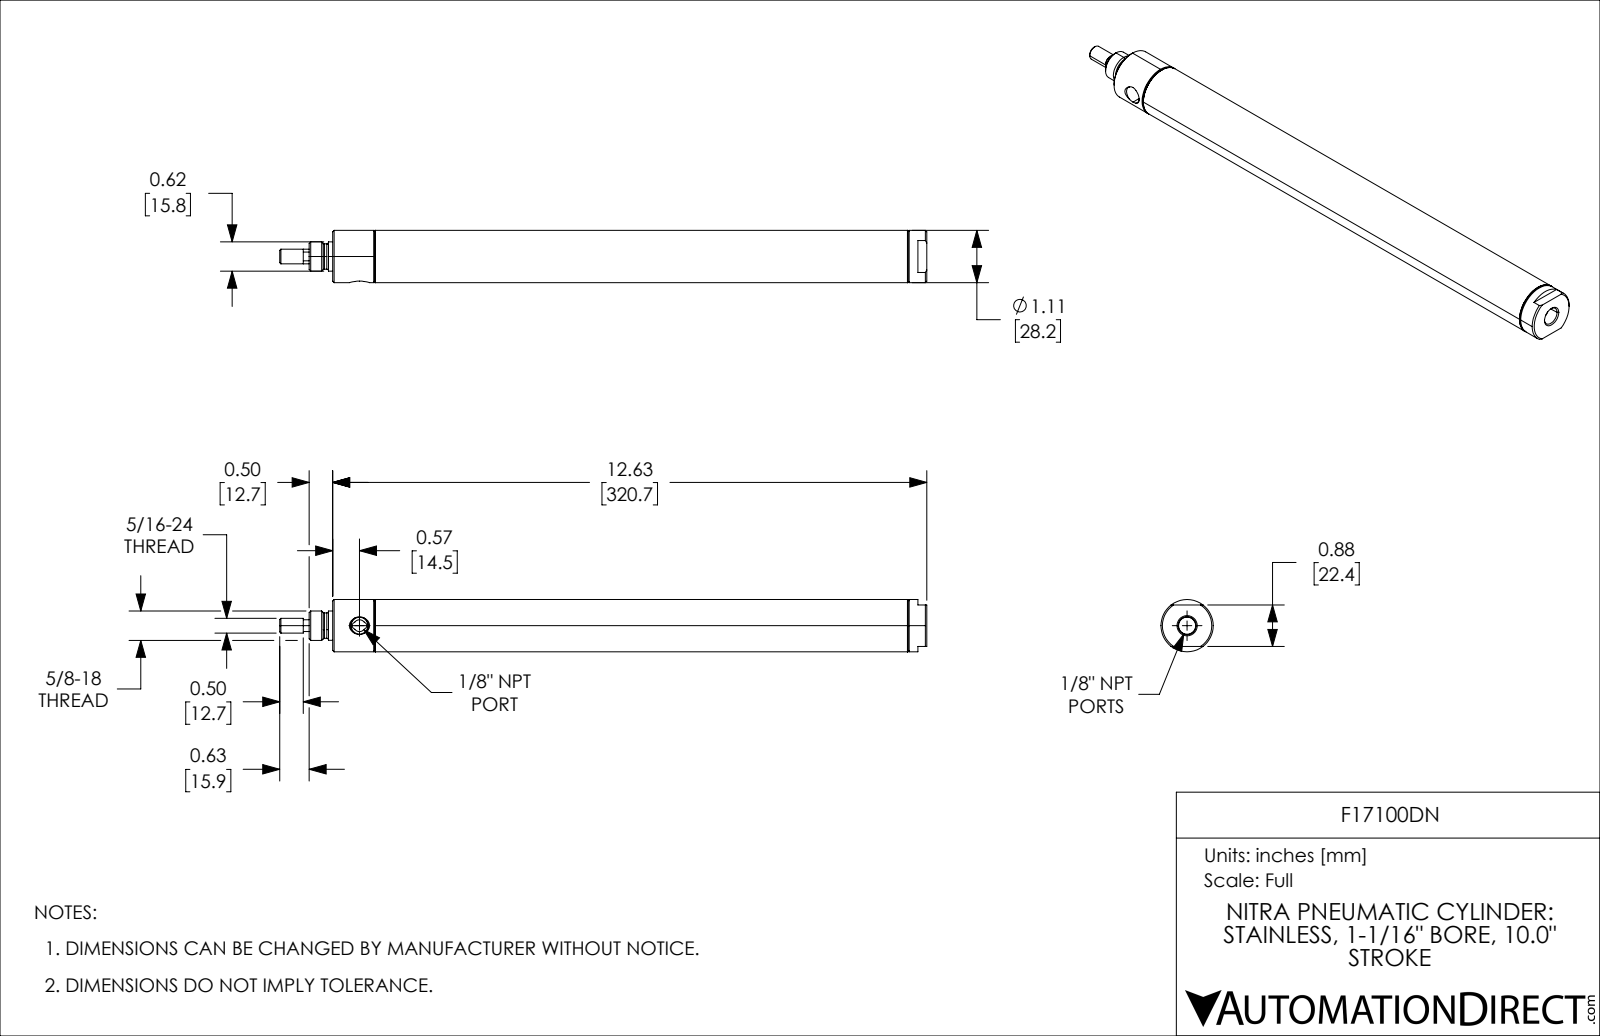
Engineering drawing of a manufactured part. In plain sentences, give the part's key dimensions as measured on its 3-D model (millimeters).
The part is named "F17100DN; F17100DN_5; F17100DN_9; F17100DN_3 (+1 more)". Its 3-D file was written by "SolidWorks 2021 (CONFIG_CONTROL_DESIGN)". It is 4 solids with 125 faces: 25 planar, 44 cylindrical and 56 other. Overall it measures 349.25 by 28.19 by 28.19 millimeters. Its volume is 63 881 cubic millimeters and its surface area 70 334 square millimeters. Round holes: 1 of diameter 8.53, 1 of diameter 9.25, 1 of diameter 19.05, 1 of diameter 25.7. Round bosses or shafts: 1 of diameter 28.19, 1 of diameter 27.23, 1 of diameter 15.88, 1 of diameter 15.81, 1 of diameter 13.68, 1 of diameter 7.94, 1 of diameter 7.92. Partial cylindrical surfaces (rounded edges, fillets, slot ends): 1 of radius 3.17. The main face-to-face distances are 22.22, 254, 276.22, 292.1, 38.1, 15.88, 28.58, 282.58, 304.8, 320.68.
